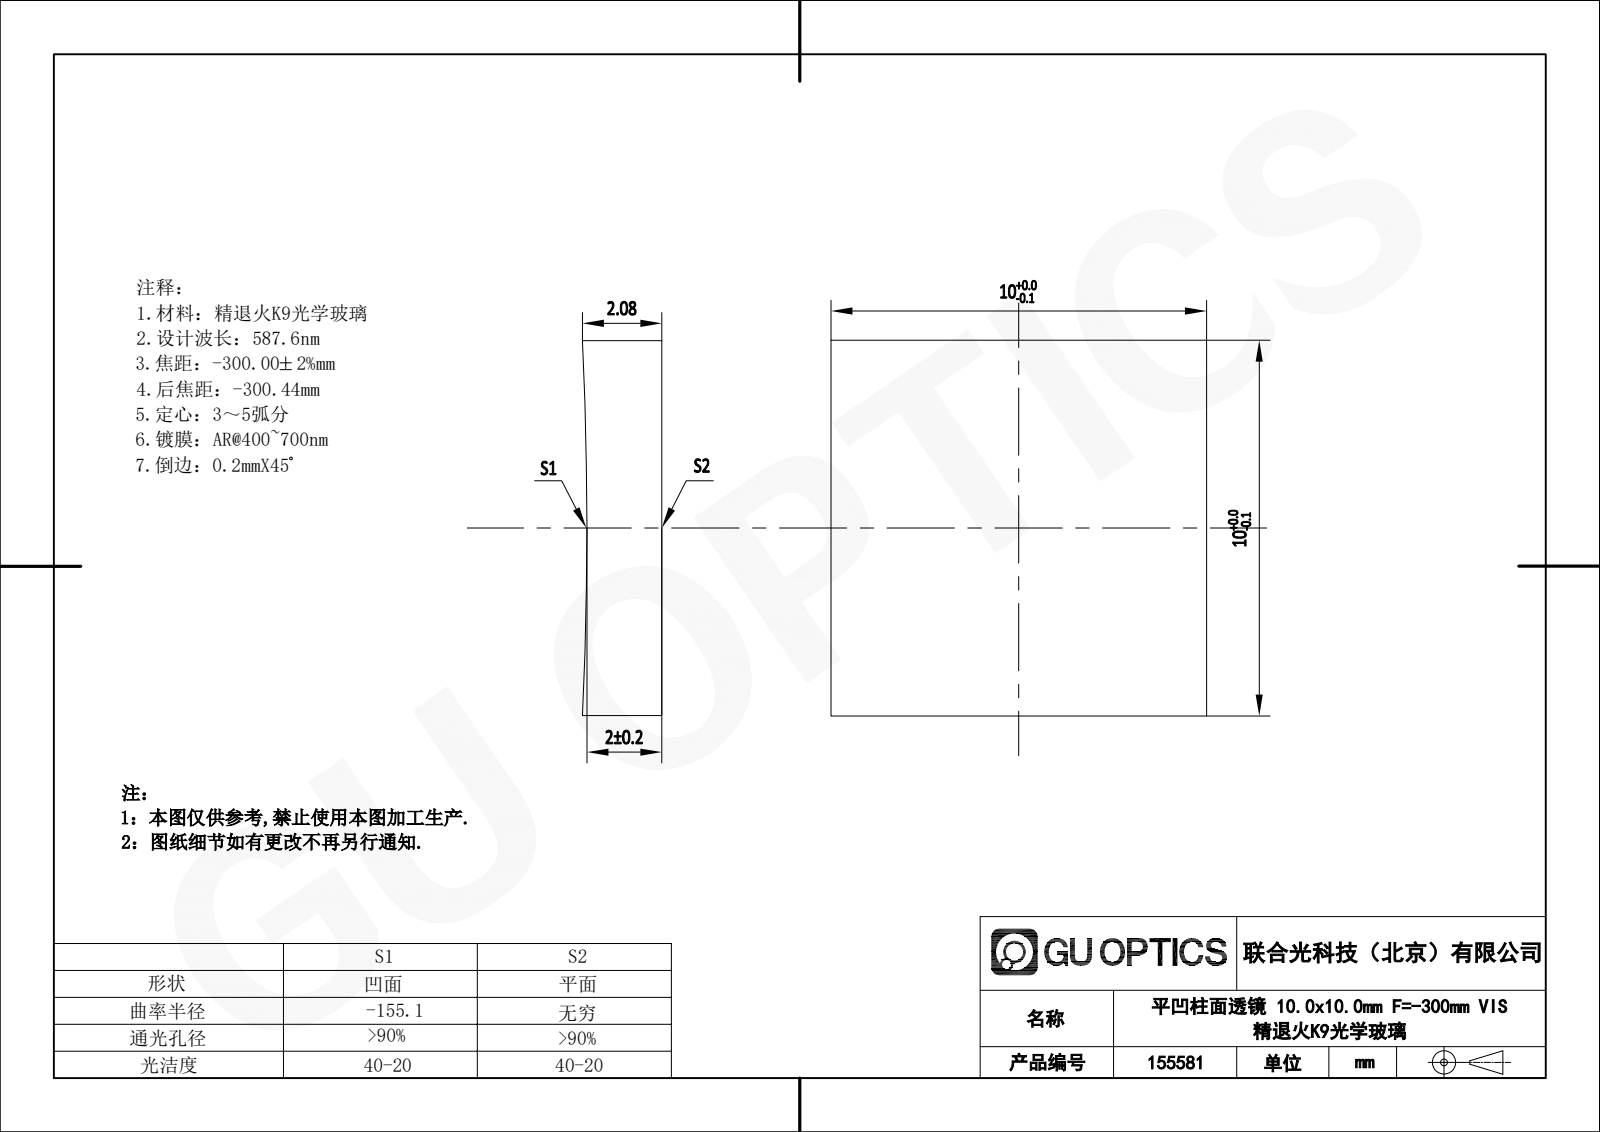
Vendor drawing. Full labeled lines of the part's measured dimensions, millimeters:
Part name (STEP PRODUCT): 155571
STEP written by: SolidWorks 2020 (CONFIG_CONTROL_DESIGN)
Units: millimetres
Bodies: 1 solid, 6 faces (5 planar, 1 cylindrical, 0 other)
Overall size (bounding box): 10 × 10 × 2.1
Volume: 204 mm³ · Surface area: 283 mm²
Partial cylindrical surfaces — rounded edges, fillets, slot ends (radius × count): R129.25 ×1
Main face-to-face distances: 10
